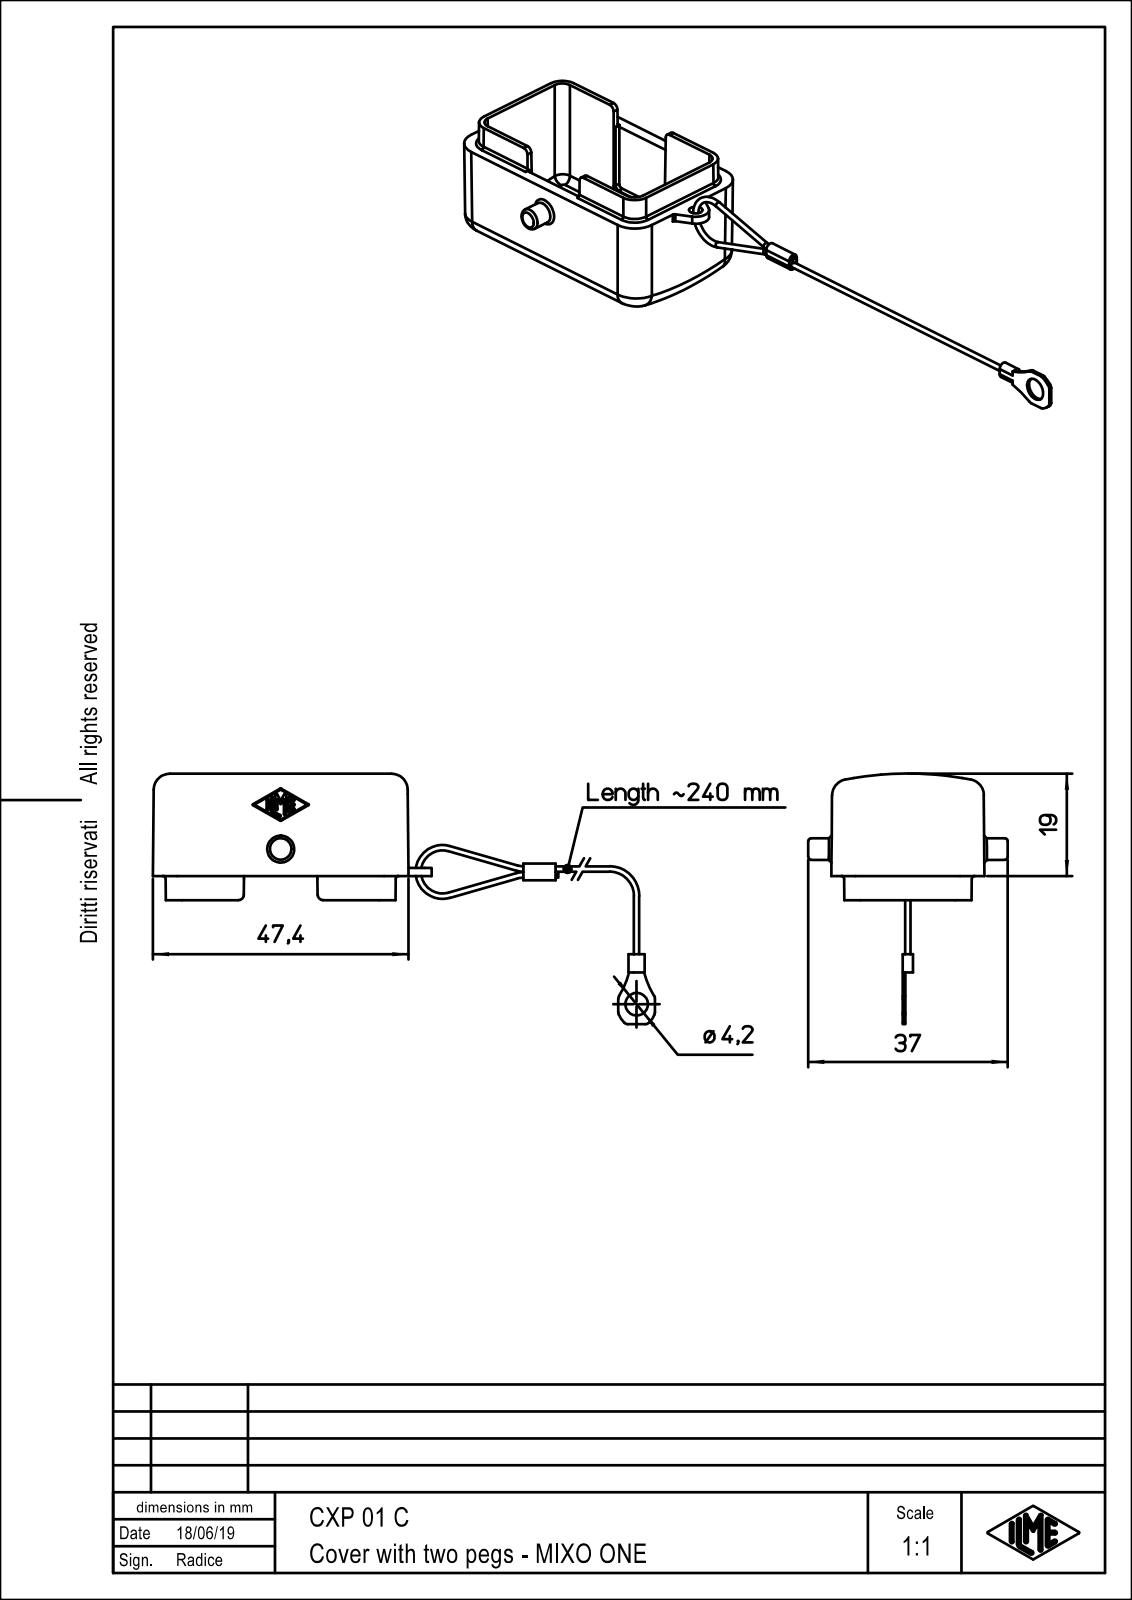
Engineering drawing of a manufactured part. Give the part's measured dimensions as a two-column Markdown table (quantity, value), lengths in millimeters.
| quantity | value |
| --- | --- |
| part name | CXP_01_C |
| STEP written by | Creo Elements/Direct Modeling 20.1B 02-Apr-2019 (C) Parametric Technology GmbH (AUTOMOTIVE_DESIGN) |
| units | millimeters |
| bodies | 1 solid, 120 faces (45 planar, 53 cylindrical, 22 other) |
| overall size | 292.9 × 37 × 23.5 |
| volume | 10 275 mm³ |
| surface area | 9 061 mm² |
| round holes (diameter × count) | 4.2 × 1 |
| round bosses / shafts (diameter × count) | 1 × 4, 4 × 1 |
| partial cylindrical surfaces (radius × count) | 1 × 8, 3 × 6, 2 × 4, 4.5 × 4, 0.5 × 2, 0.95 × 2, 5 × 2, 15 × 2 |
| main face-to-face distances | 3.44, 2.4, 1.04, 26.04, 23.64, 22.6, 45.04, 41.6, 4.5, 16.89 |
